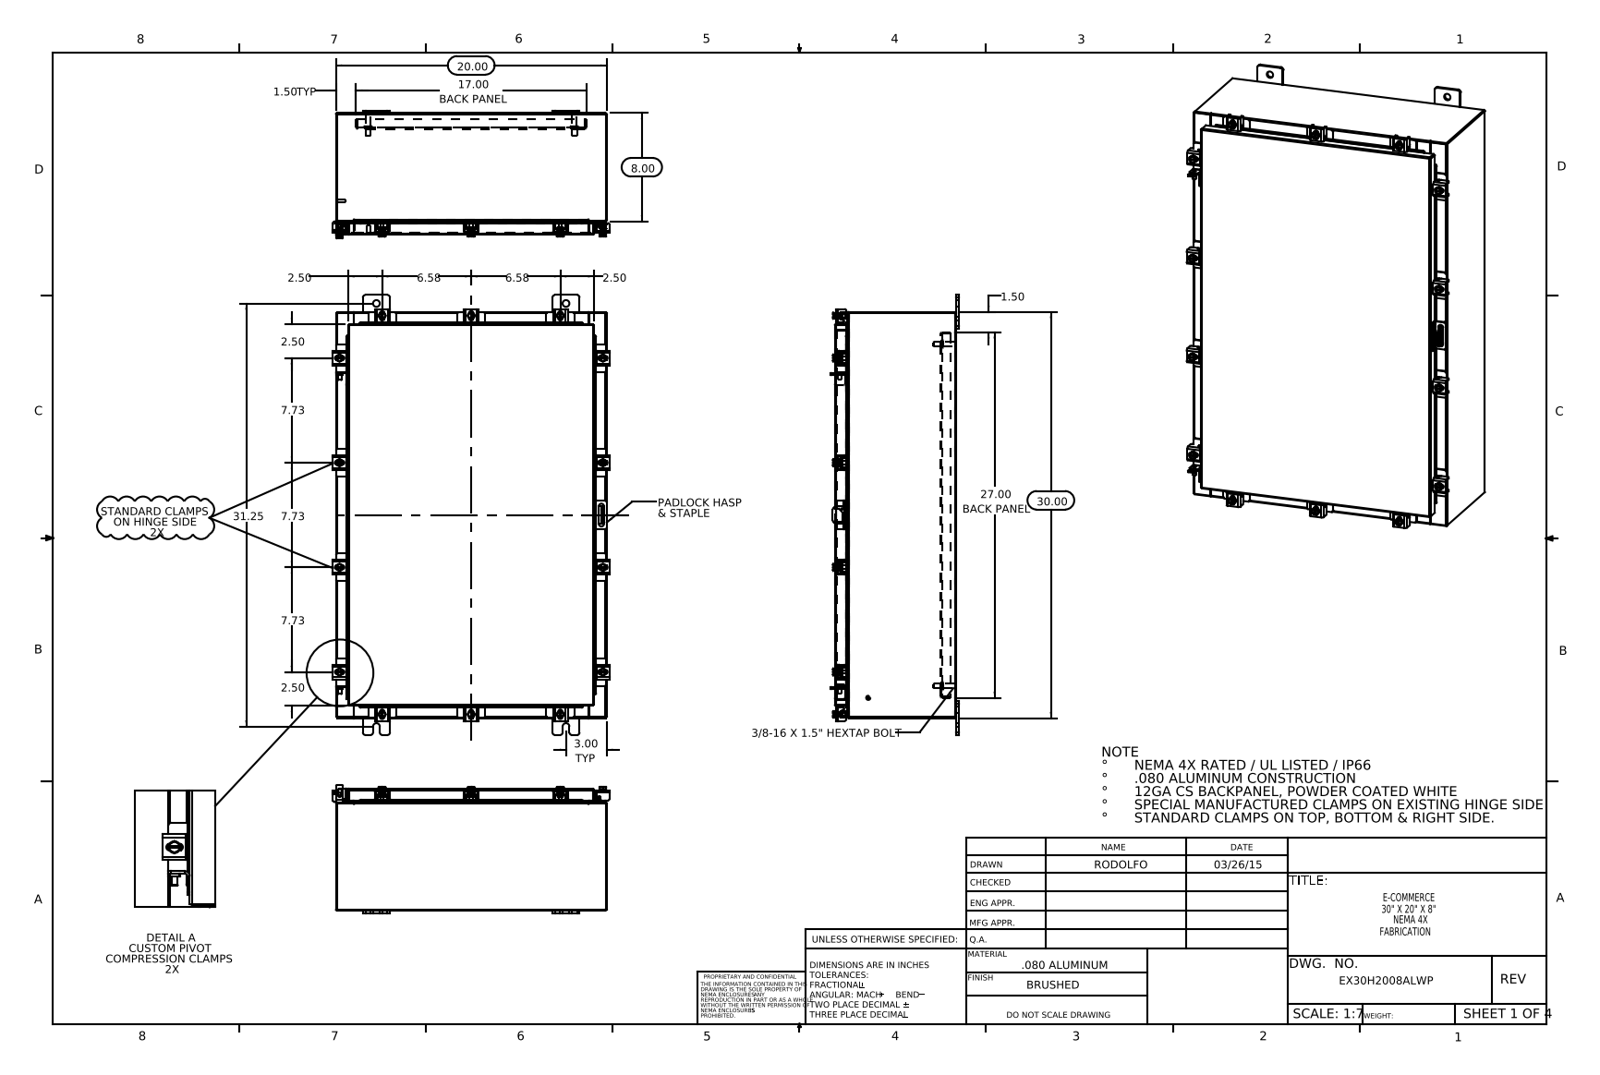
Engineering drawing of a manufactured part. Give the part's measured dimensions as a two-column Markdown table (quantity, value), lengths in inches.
| quantity | value |
| --- | --- |
| part name | EX30H2008ALWP Cover; EX30H2008ALWP Padlock Staple; EX30H2008ALWP; EX30H2008ALWP Clamp Bracket (+8 more) |
| STEP written by | SolidWorks 2014 (CONFIG_CONTROL_DESIGN) |
| units | inches |
| bodies | 91 solids, 2272 faces (1211 planar, 885 cylindrical, 176 other) |
| overall size | 32.5 × 20.421 × 9.453 |
| volume | 228.8 in³ |
| surface area | 5 700 in² |
| round holes (diameter × count) | 0.213 × 14, 0.26 × 14, 0.5 × 8, 0.125 × 1, 0.25 × 1 |
| round bosses / shafts (diameter × count) | 0.5 × 14, 0.25 × 14, 0.399 × 12, 0.625 × 4, 0.375 × 4, 0.33 × 4, 0.315 × 2, 0.236 × 2 |
| partial cylindrical surfaces (radius × count) | 0.06 × 62, 0.141 × 28, 0.013 × 26, 0.12 × 26, 0.19 × 24, 0.088 × 22, 0.09 × 20, 0.05 × 19 |
| main face-to-face distances | 0.075, 8.9, 8.975, 8.826, 0.104, 19.925, 1, 1.075, 7.826, 7.9 |
| hole center spacings | 2.347, 4.44, 16.602, 19.451, 24.31, 26.507, 27.371, 29.793 |
